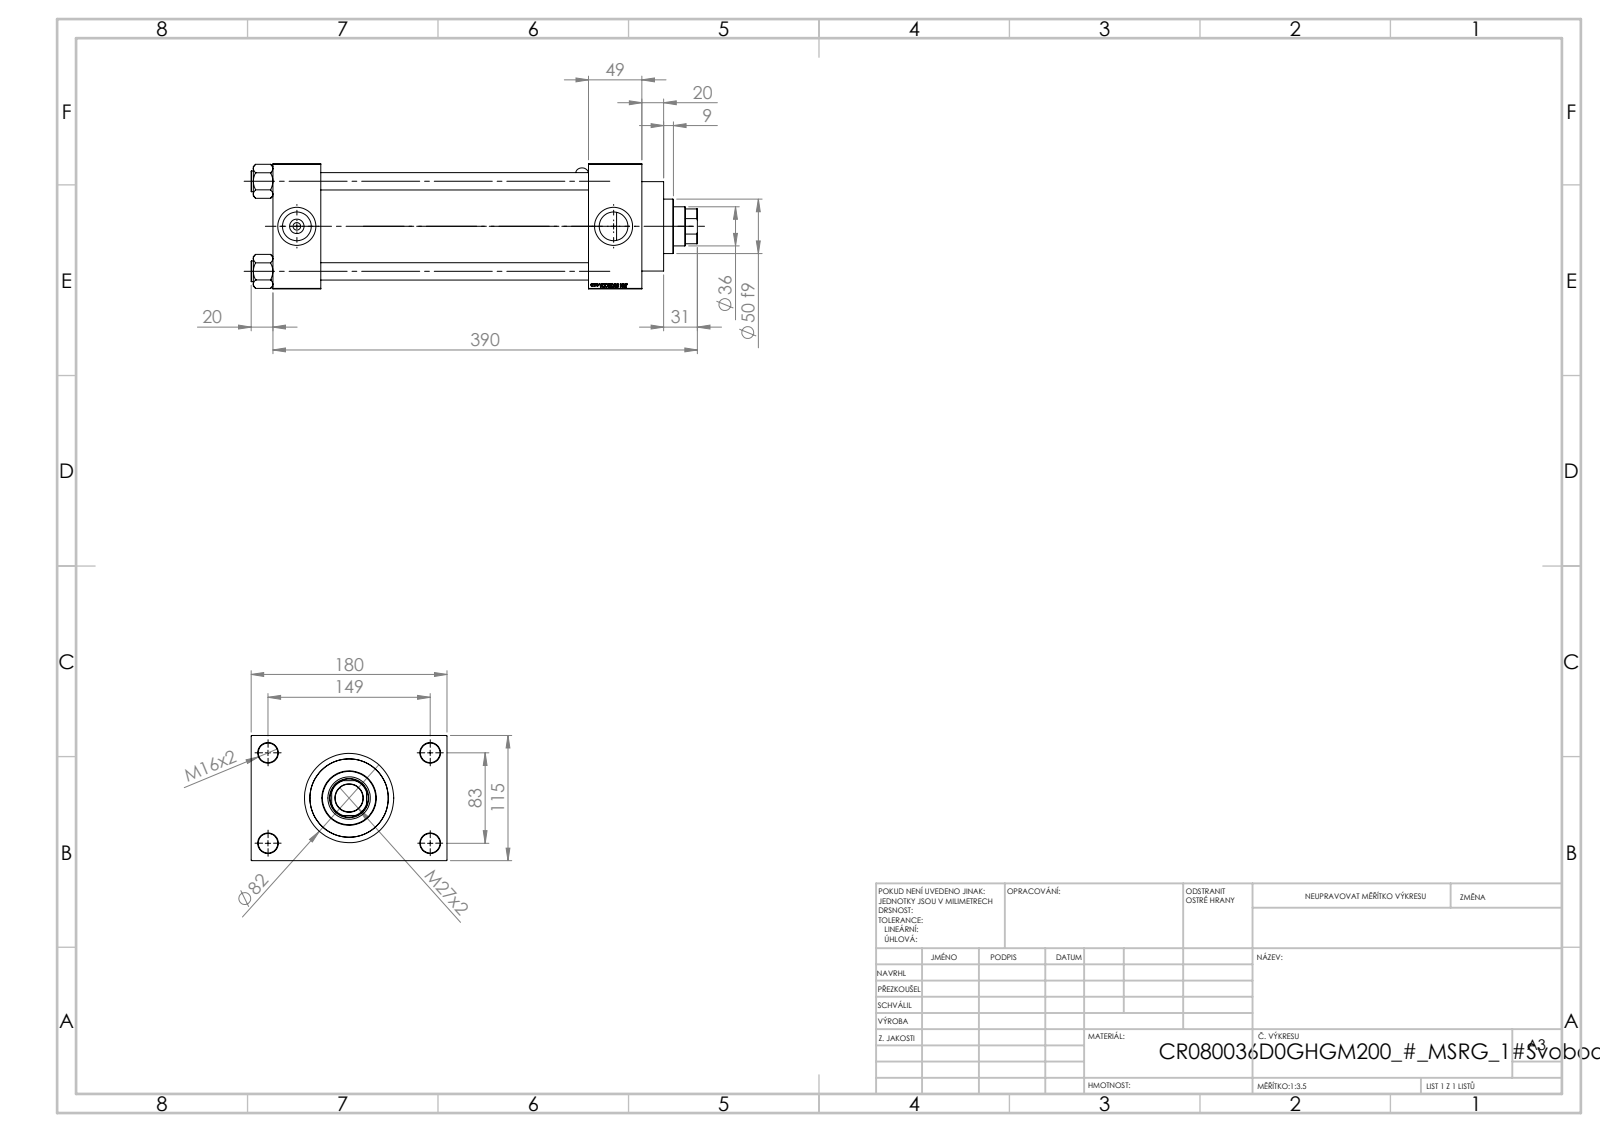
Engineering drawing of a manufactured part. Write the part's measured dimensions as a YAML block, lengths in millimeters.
part_name: "MSRF_MSRG1; V215_VC_A; V215CR_D_TYCINKA; NUT_M5_D (+2 more)"
step_written_by: "SolidWorks 2019 (CONFIG_CONTROL_DESIGN)"
units: millimeters
bodies: {solids: 12, faces: 1183, planar: 563, cylindrical: 102, other: 518}
overall_size: [410, 180, 115]
volume: 2452000
surface_area: 449368
round_holes:
  - {diameter: 16, count: 4}
  - {diameter: 18, count: 4}
  - {diameter: 7, count: 2}
  - {diameter: 26.44, count: 2}
  - {diameter: 35, count: 2}
  - {diameter: 25.5, count: 1}
  - {diameter: 36, count: 1}
  - {diameter: 39, count: 1}
  - {diameter: 61, count: 1}
  - {diameter: 72, count: 1}
  - {diameter: 80, count: 1}
round_bosses_or_shafts:
  - {diameter: 19, count: 4}
  - {diameter: 86, count: 1}
  - {diameter: 82, count: 1}
  - {diameter: 50, count: 1}
  - {diameter: 5, count: 1}
  - {diameter: 2.5, count: 1}
partial_cylinders:
  - {radius: 0.5, count: 6}
  - {radius: 6, count: 2}
  - {radius: 17.5, count: 1}
face_to_face_distances: [115, 246, 295, 49, 44, 290, 339, 32.5, 147.5, 180]
hole_center_spacings: [33.15, 58.48, 82.7, 85.28, 89.24, 115.85, 142.43, 83]
